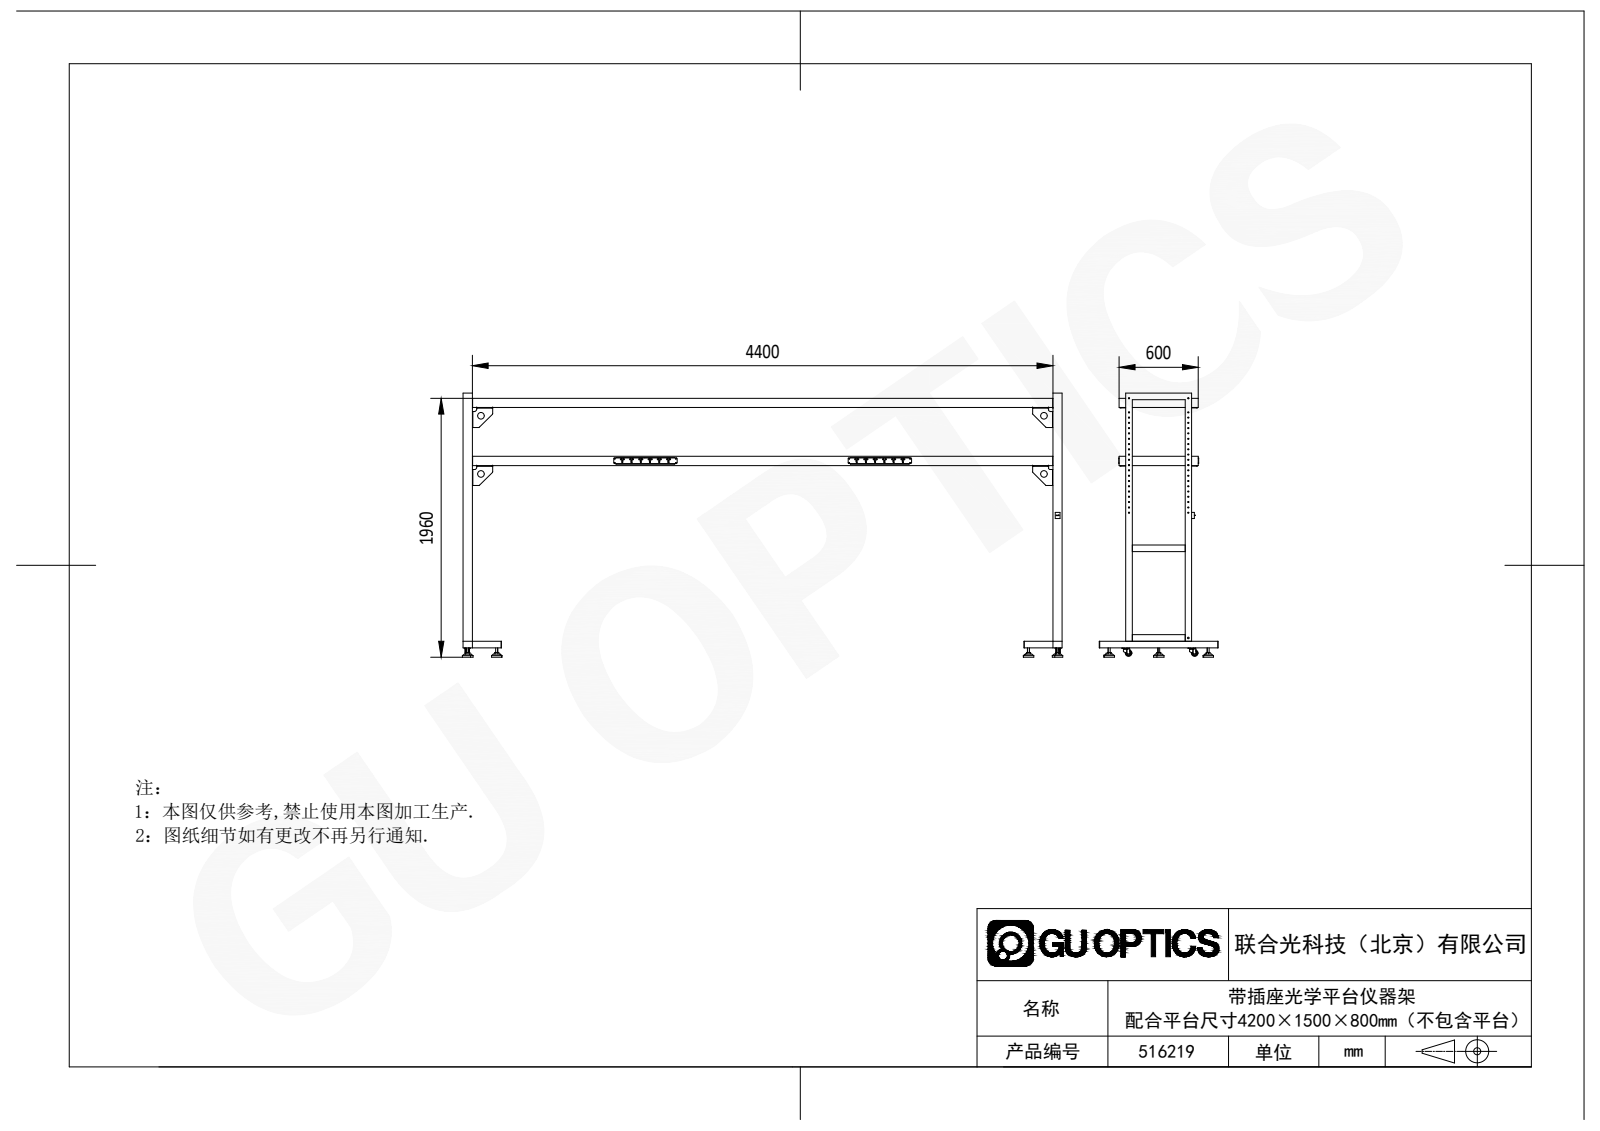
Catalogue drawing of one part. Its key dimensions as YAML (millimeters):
part_name: "516219"
step_written_by: "SolidWorks 2020 (CONFIG_CONTROL_DESIGN)"
units: millimeters
bodies: {solids: 55, faces: 2593, planar: 1445, cylindrical: 1072, other: 76}
overall_size: [4550, 2001, 900]
volume: 33320000
surface_area: 25170000
round_holes:
  - {diameter: 9, count: 66}
  - {diameter: 6.1, count: 16}
  - {diameter: 10, count: 16}
  - {diameter: 6.5, count: 12}
  - {diameter: 4.2, count: 8}
  - {diameter: 5.2, count: 8}
  - {diameter: 6, count: 8}
  - {diameter: 17, count: 6}
  - {diameter: 18, count: 6}
  - {diameter: 26, count: 6}
  - {diameter: 69, count: 6}
  - {diameter: 3.2, count: 4}
round_bosses_or_shafts:
  - {diameter: 80, count: 6}
  - {diameter: 16, count: 6}
  - {diameter: 26, count: 4}
  - {diameter: 18, count: 4}
  - {diameter: 50, count: 2}
  - {diameter: 10, count: 2}
partial_cylinders:
  - {radius: 5, count: 36}
  - {radius: 7, count: 24}
  - {radius: 3, count: 16}
  - {radius: 4.25, count: 12}
  - {radius: 1.5, count: 8}
  - {radius: 1.51, count: 8}
  - {radius: 4.01, count: 8}
  - {radius: 13, count: 4}
face_to_face_distances: [440, 1.5, 3, 70, 67, 438.5, 2.5, 67.5, 441.5, 530]
hole_center_spacings: [40, 80, 120, 280, 160, 200, 240, 320]
